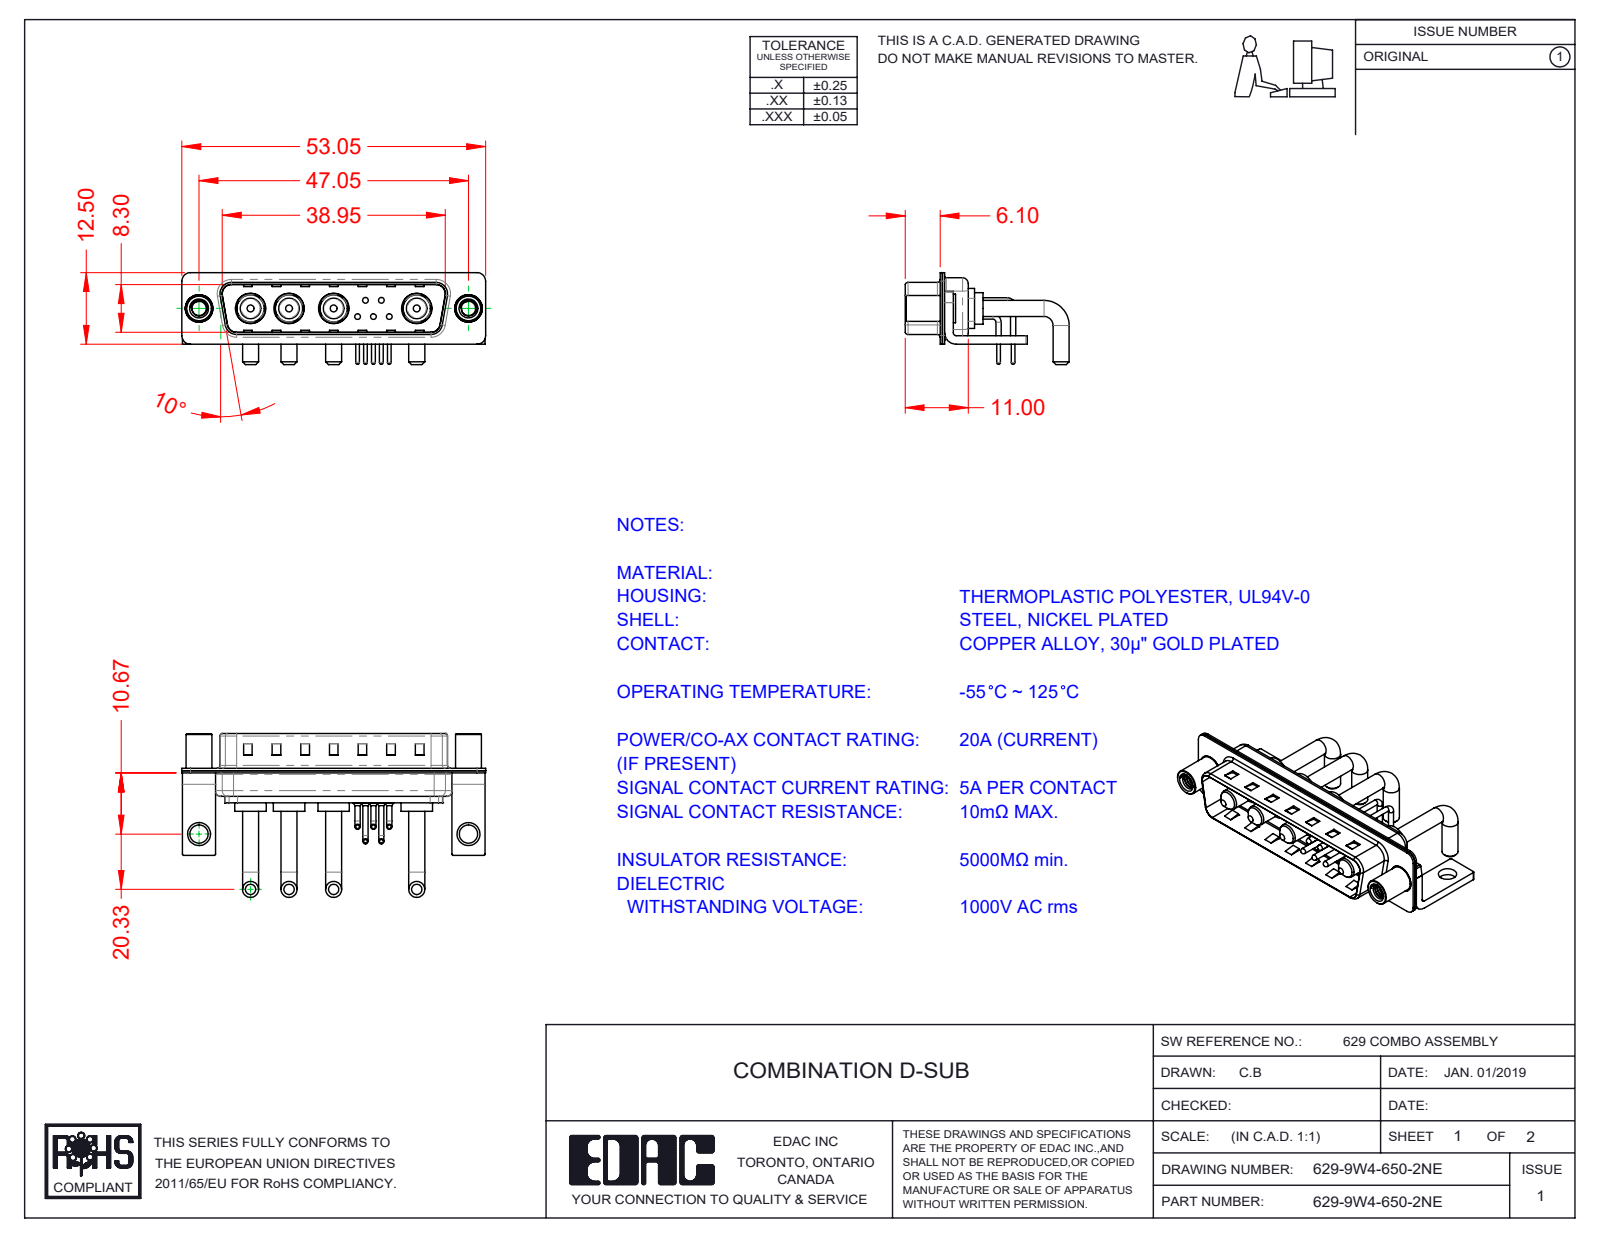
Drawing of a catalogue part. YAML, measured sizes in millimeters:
part_name: "Power Pin_Ext 20A RA; 629Combo Stabilizer Bracket; 629-9W4-650-2NE; 629Combo Contact Row 2 (+5 more)"
step_written_by: "SolidWorks 2020 (CONFIG_CONTROL_DESIGN)"
units: millimeters
bodies: {solids: 20, faces: 1196, planar: 553, cylindrical: 473, other: 170}
overall_size: [53.05, 28.63, 16.05]
volume: 3863
surface_area: 8426
round_holes:
  - {diameter: 0.75, count: 5}
  - {diameter: 1.6, count: 5}
  - {diameter: 2, count: 5}
  - {diameter: 4.85, count: 4}
  - {diameter: 5.3, count: 4}
  - {diameter: 2.5, count: 2}
  - {diameter: 3.2, count: 2}
  - {diameter: 4, count: 2}
  - {diameter: 4.8, count: 2}
round_bosses_or_shafts:
  - {diameter: 0.9, count: 10}
  - {diameter: 2.8, count: 8}
  - {diameter: 1.5, count: 5}
  - {diameter: 1, count: 5}
  - {diameter: 0.65, count: 5}
  - {diameter: 5.5, count: 4}
  - {diameter: 5.2, count: 4}
  - {diameter: 4.75, count: 4}
partial_cylinders:
  - {radius: 0.25, count: 16}
  - {radius: 1.5, count: 16}
  - {radius: 2, count: 13}
  - {radius: 0.5, count: 9}
  - {radius: 1.6, count: 8}
  - {radius: 1.01, count: 5}
  - {radius: 0.6, count: 4}
  - {radius: 0.65, count: 4}
face_to_face_distances: [0.4, 0.8, 9.5, 1.5, 9.1, 8.7, 9.9, 5.2, 0.75, 1.2]
hole_center_spacings: [3.16, 2.77, 5.04, 14.5, 47.05, 2.78, 4.4, 4.41]
